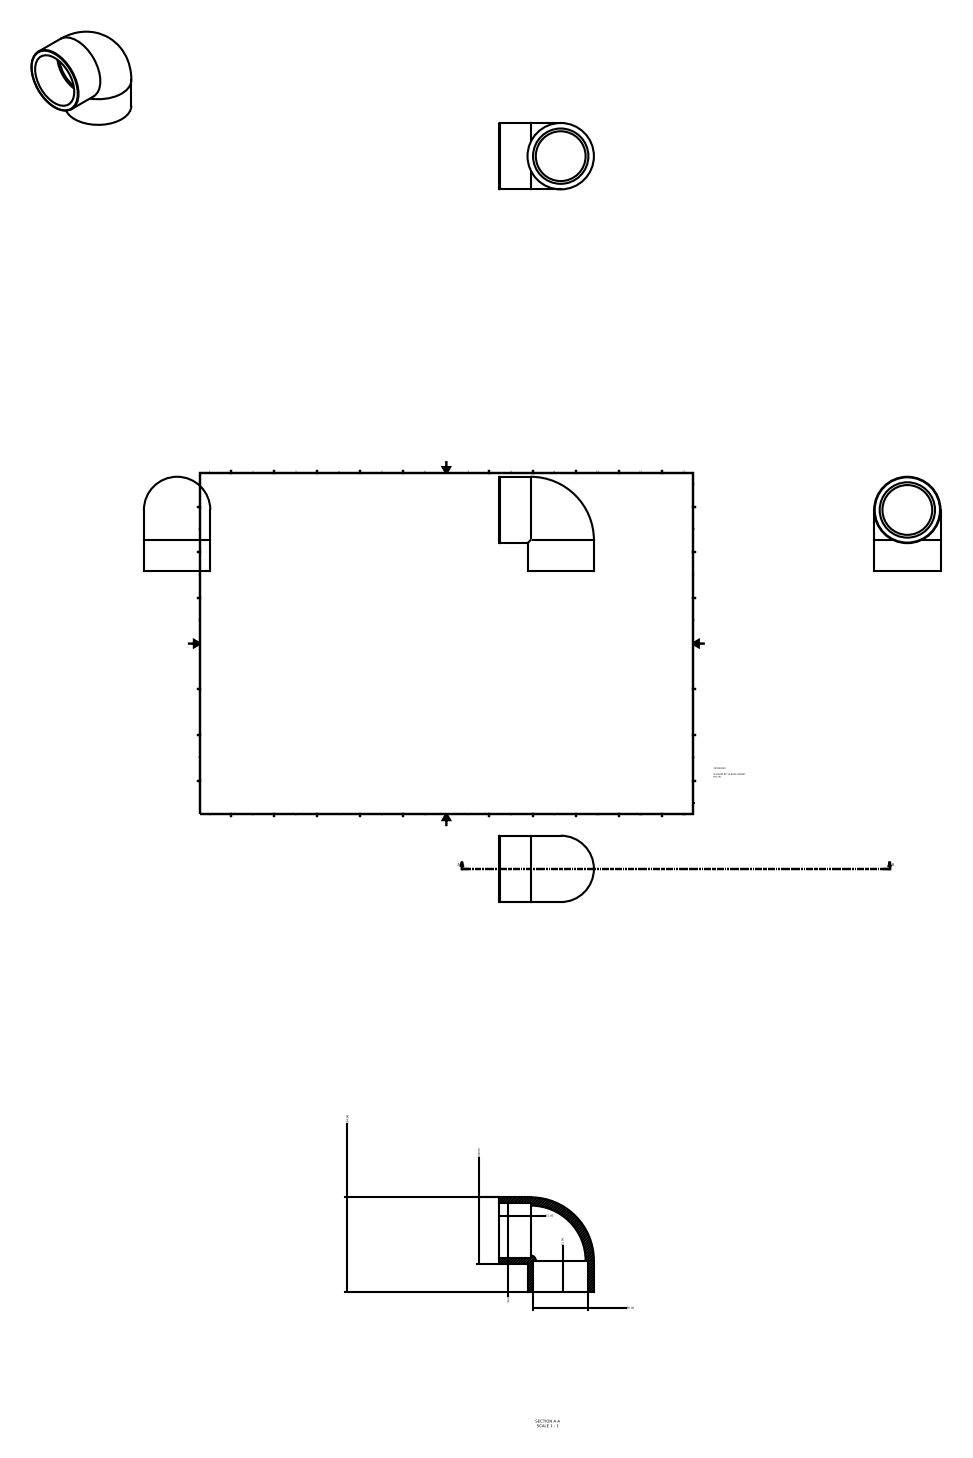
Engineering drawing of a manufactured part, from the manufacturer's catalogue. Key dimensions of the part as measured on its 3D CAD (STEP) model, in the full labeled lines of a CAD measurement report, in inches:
Part name (STEP PRODUCT): 050500090
STEP written by: Autodesk Inventor 2015 (AUTOMOTIVE_DESIGN)
Units: inches
Bodies: 1 solid, 11 faces (4 planar, 4 cylindrical, 3 other)
Overall size (bounding box): 6.063 × 6.063 × 4.252
Volume: 36.71 in³ · Surface area: 181.4 in²
Round holes (diameter × count): ⌀3.543 ×2
Round bosses / shafts (diameter × count): ⌀4.252 ×2
Main face-to-face distances: 2.008
